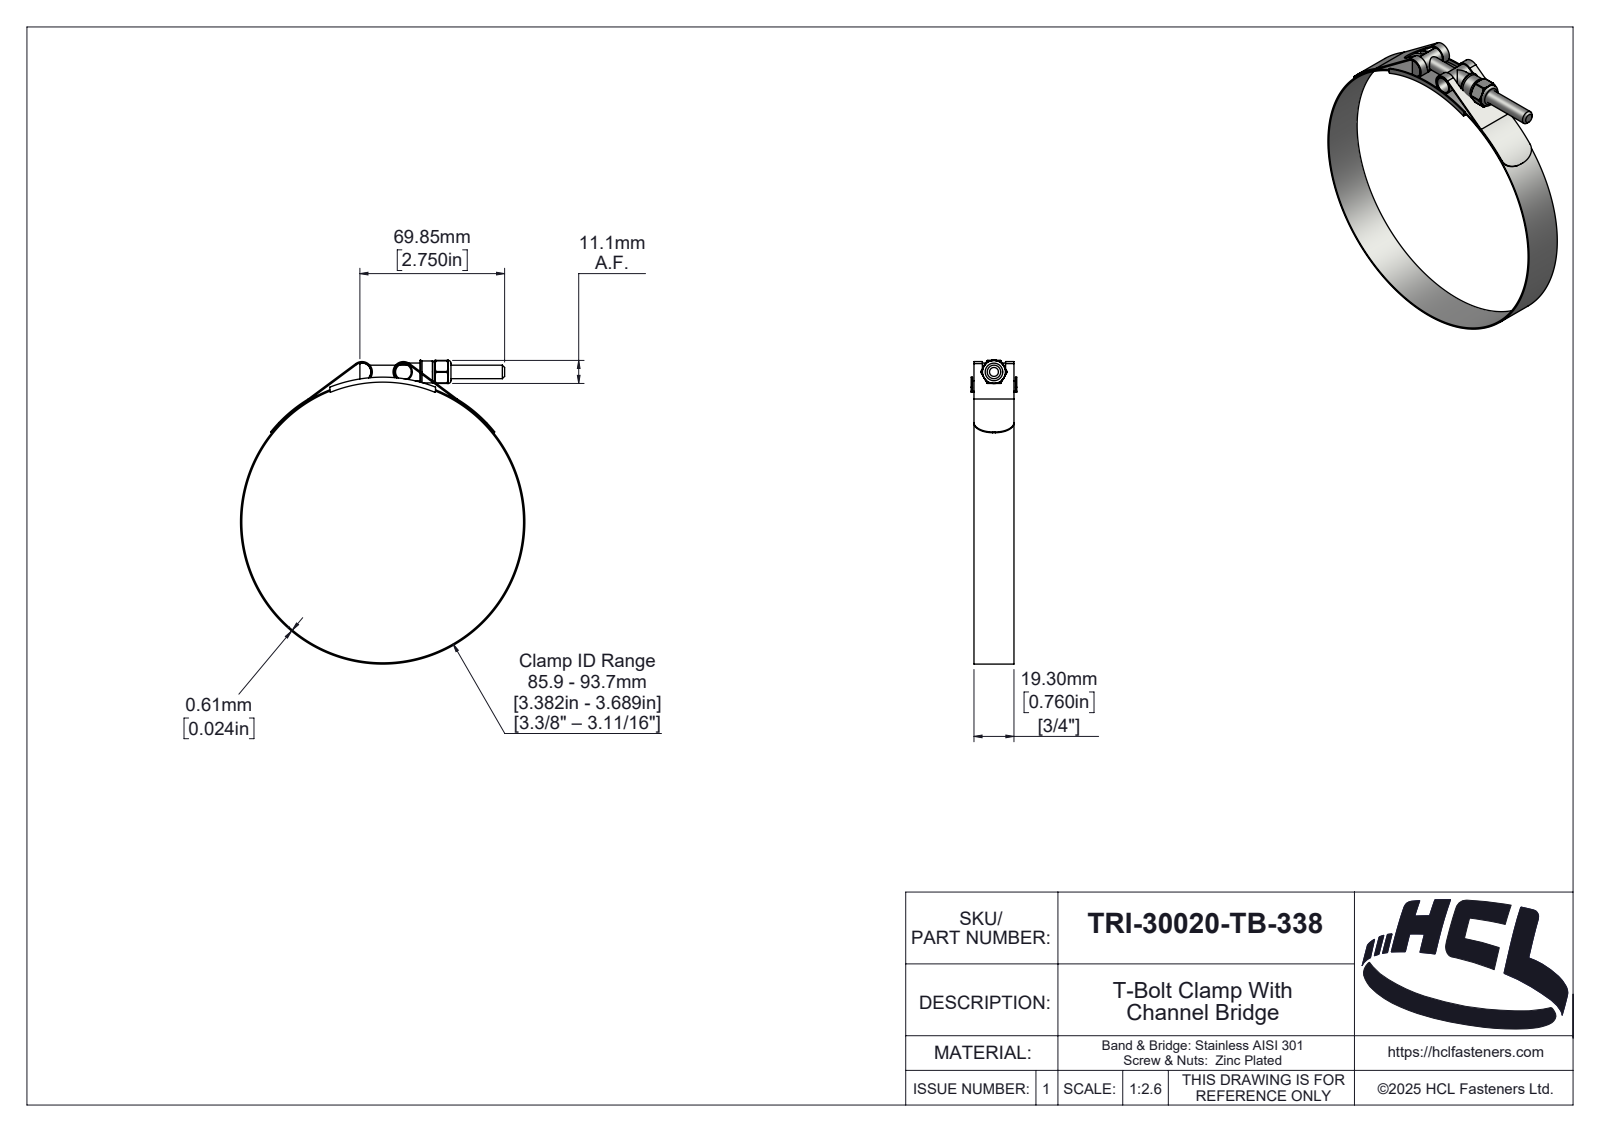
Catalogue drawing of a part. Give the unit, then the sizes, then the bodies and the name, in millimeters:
Units: millimetres
Overall size (bounding box): 146.64 × 137.22 × 22
Round holes (diameter × count): ⌀5.4 ×1, ⌀6.35 ×1, ⌀6.5 ×1, ⌀7.58 ×1, ⌀136 ×1
Round bosses / shafts (diameter × count): ⌀8.58 ×2, ⌀137.22 ×1, ⌀10.58 ×1
Partial cylindrical surfaces — rounded edges, fillets, slot ends (radius × count): R0.39 ×6, R0.5 ×2, R4.39 ×2, R5 ×2, R0.59 ×1, R2.42 ×1, R3.03 ×1, R3.19 ×1
Main face-to-face distances: 0.61, 19.3, 1.35, 20.65, 0.74, 21.39, 20.04, 22, 11.11, 20.78
Hole centre spacings: 73
Volume: 11 078 mm³ · Surface area: 27 805 mm²
Bodies: 6 solids, 330 faces (44 planar, 122 cylindrical, 164 other)
Part name (STEP PRODUCT): TRI-30020-TB-338
STEP written by: SolidWorks 2025 (AUTOMOTIVE_DESIGN)
